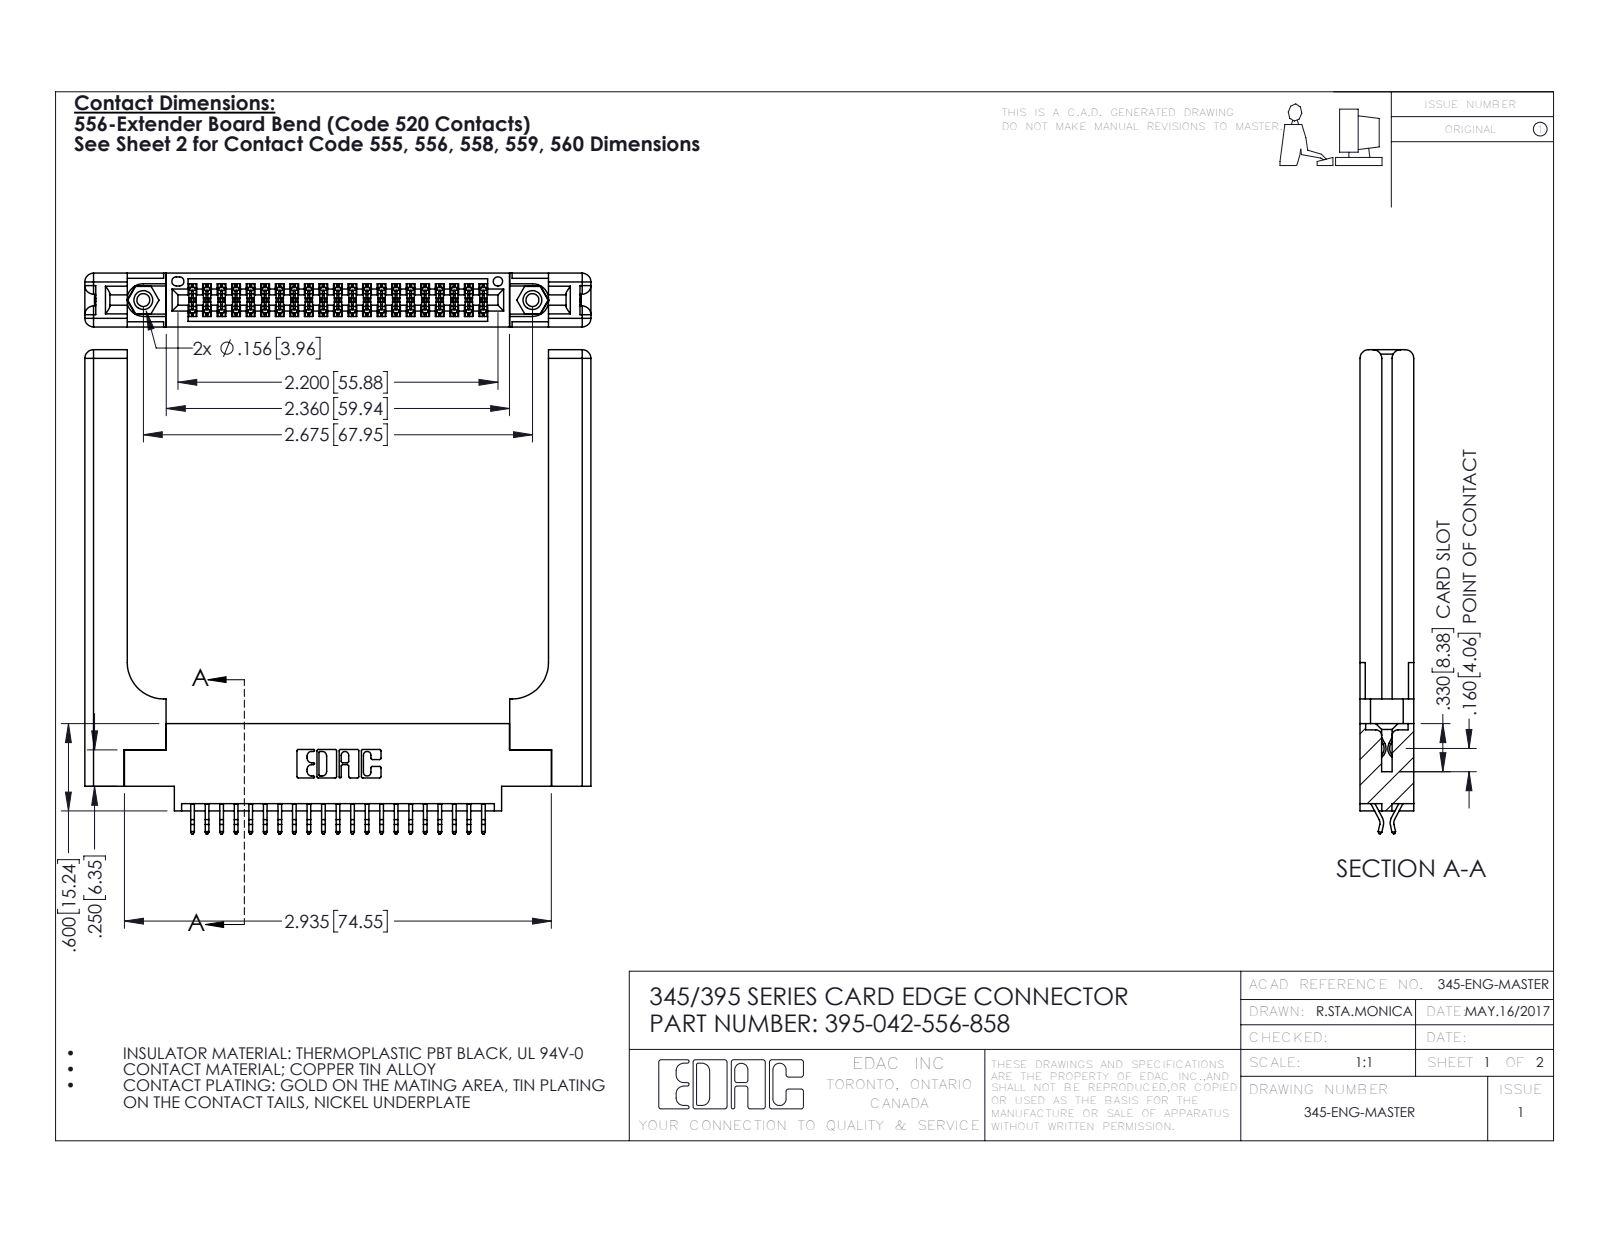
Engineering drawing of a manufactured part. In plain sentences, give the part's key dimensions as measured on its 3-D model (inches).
The part is named "345-220-058_345-220-058; 345-250-001_345-250-001-102; 345-292-001_556 Tail; 345 Part_0.170 Offset - 0.156 Dia-TH (+1 more)". Its 3-D file was written by "SolidWorks 2016 (CONFIG_CONTROL_DESIGN)". It is 47 solids with 2738 faces: 1786 planar, 892 cylindrical and 60 other. Overall it measures 3.479 by 3.327 by 0.37 inches. Its volume is 1.022 cubic inches and its surface area 26.33 square inches. Round holes: 2 of diameter 0.089, 2 of diameter 0.125, 2 of diameter 0.156, 1 of diameter 0.064. Round bosses or shafts: 2 of diameter 0.155. Partial cylindrical surfaces (rounded edges, fillets, slot ends): 63 of radius 0.006, 22 of radius 0.01, 16 of radius 0.06, 6 of radius 0.007, 6 of radius 0.031, 3 of radius 0.026, 2 of radius 0.01, 2 of radius 0.014. The main face-to-face distances are 0.37, 0.072, 0.298, 0.148, 0.15, 0.077, 0.225, 0.22, 0.025, 0.123. The hole center spacings are 0.27, 2.441, 2.675.
